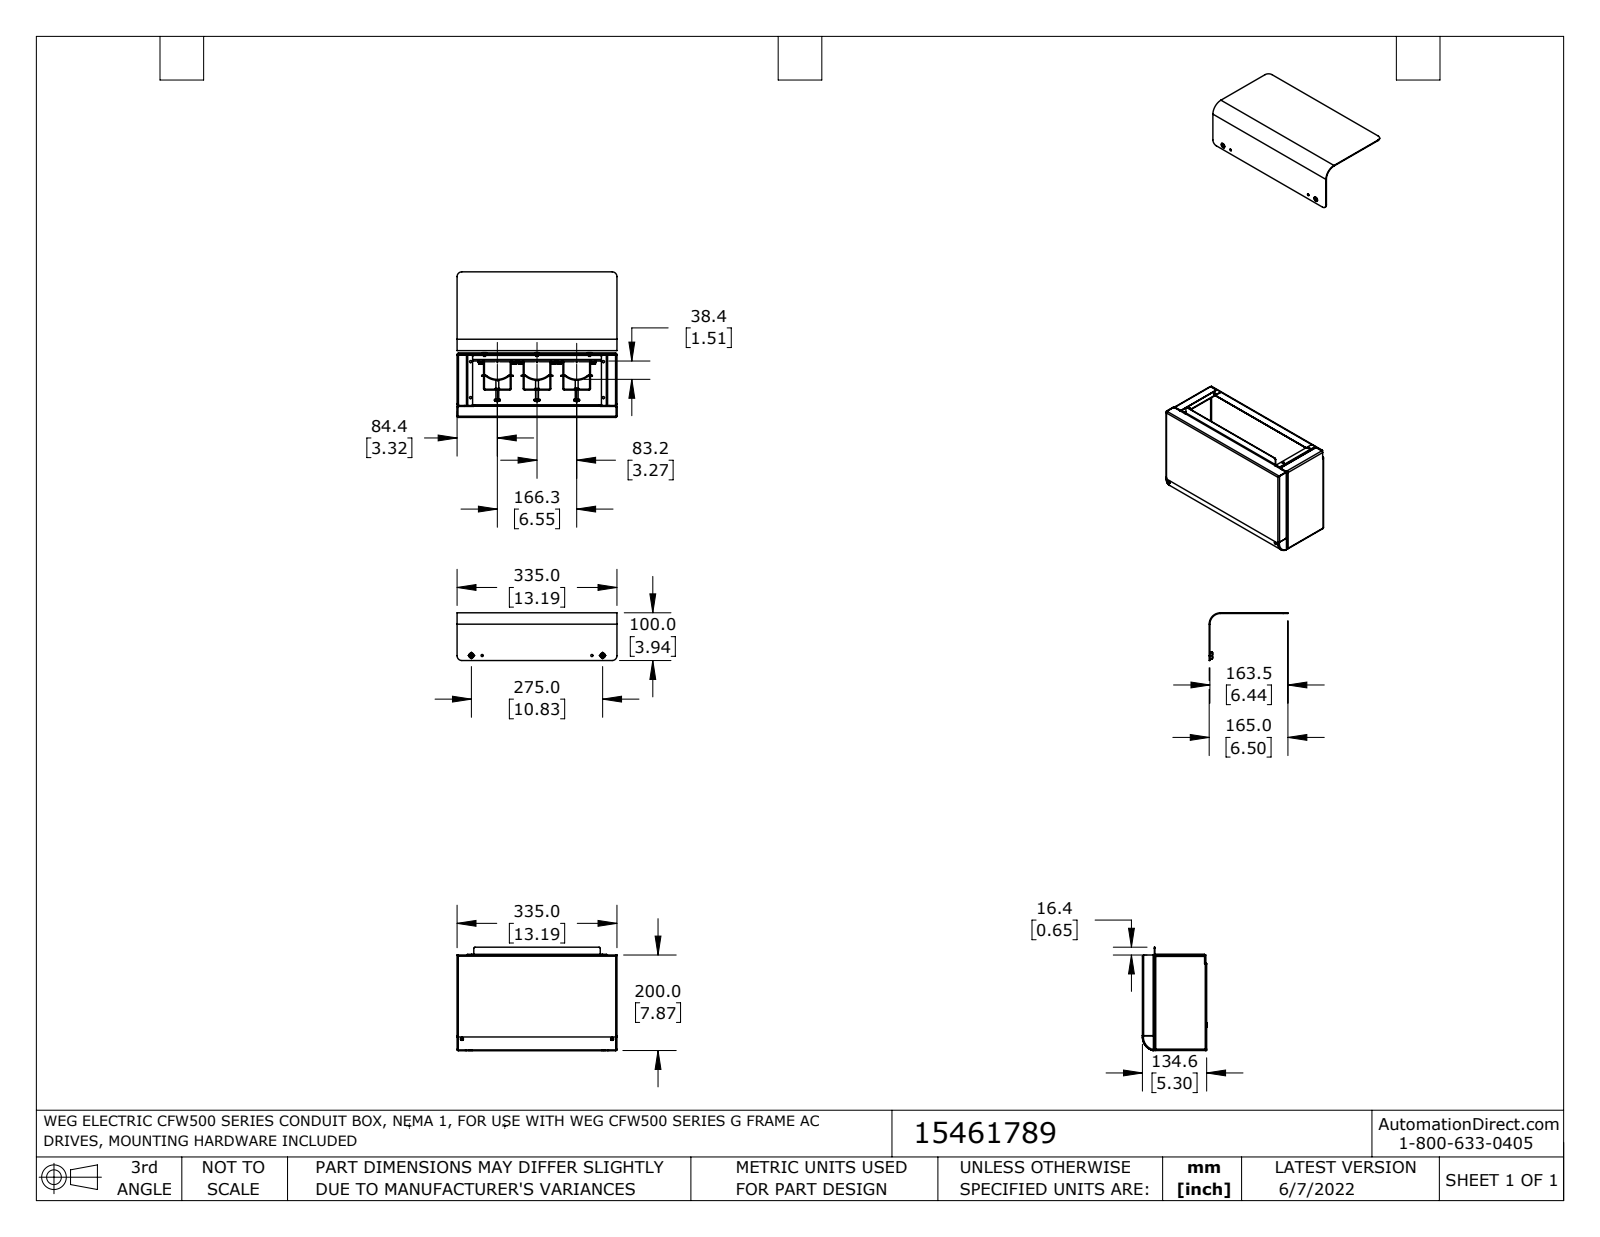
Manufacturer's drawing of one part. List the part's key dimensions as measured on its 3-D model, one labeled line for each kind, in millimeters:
Part name (STEP PRODUCT): 15461789_CFW500-KN1G
STEP written by: SolidWorks 2021 (AUTOMOTIVE_DESIGN)
Units: millimetres
Bodies: 34 solids, 1651 faces (798 planar, 464 cylindrical, 389 other)
Overall size (bounding box): 916.8 × 335 × 304.9
Volume: 472 600 mm³ · Surface area: 700 000 mm²
Round holes (diameter × count): ⌀3.2 ×11, ⌀5.5 ×9, ⌀3.5 ×6, ⌀3.7 ×6, ⌀4.5 ×6, ⌀5.8 ×6, ⌀5 ×3, ⌀2.5 ×2, ⌀4.2 ×2, ⌀5.2 ×2, ⌀6.8 ×2, ⌀8 ×2
Round bosses / shafts (diameter × count): ⌀6.2 ×11, ⌀4 ×9, ⌀8.4 ×7, ⌀8.9 ×6, ⌀6.6 ×6, ⌀3.9 ×6, ⌀3.3 ×6, ⌀12 ×3
Partial cylindrical surfaces — rounded edges, fillets, slot ends (radius × count): R2.5 ×58, R0.3 ×18, R3.1 ×16, R2 ×14, R1.2 ×12, R0.5 ×10, R1.4 ×8, R2.9 ×8
Main face-to-face distances: 1.5, 1, 133.6, 132.1, 134.6, 133.1, 6.8, 333.5, 8.3, 24
Hole centre spacings: 35.6, 83.2, 278.5, 314.6, 39.7, 47.6, 74.8, 110.1
